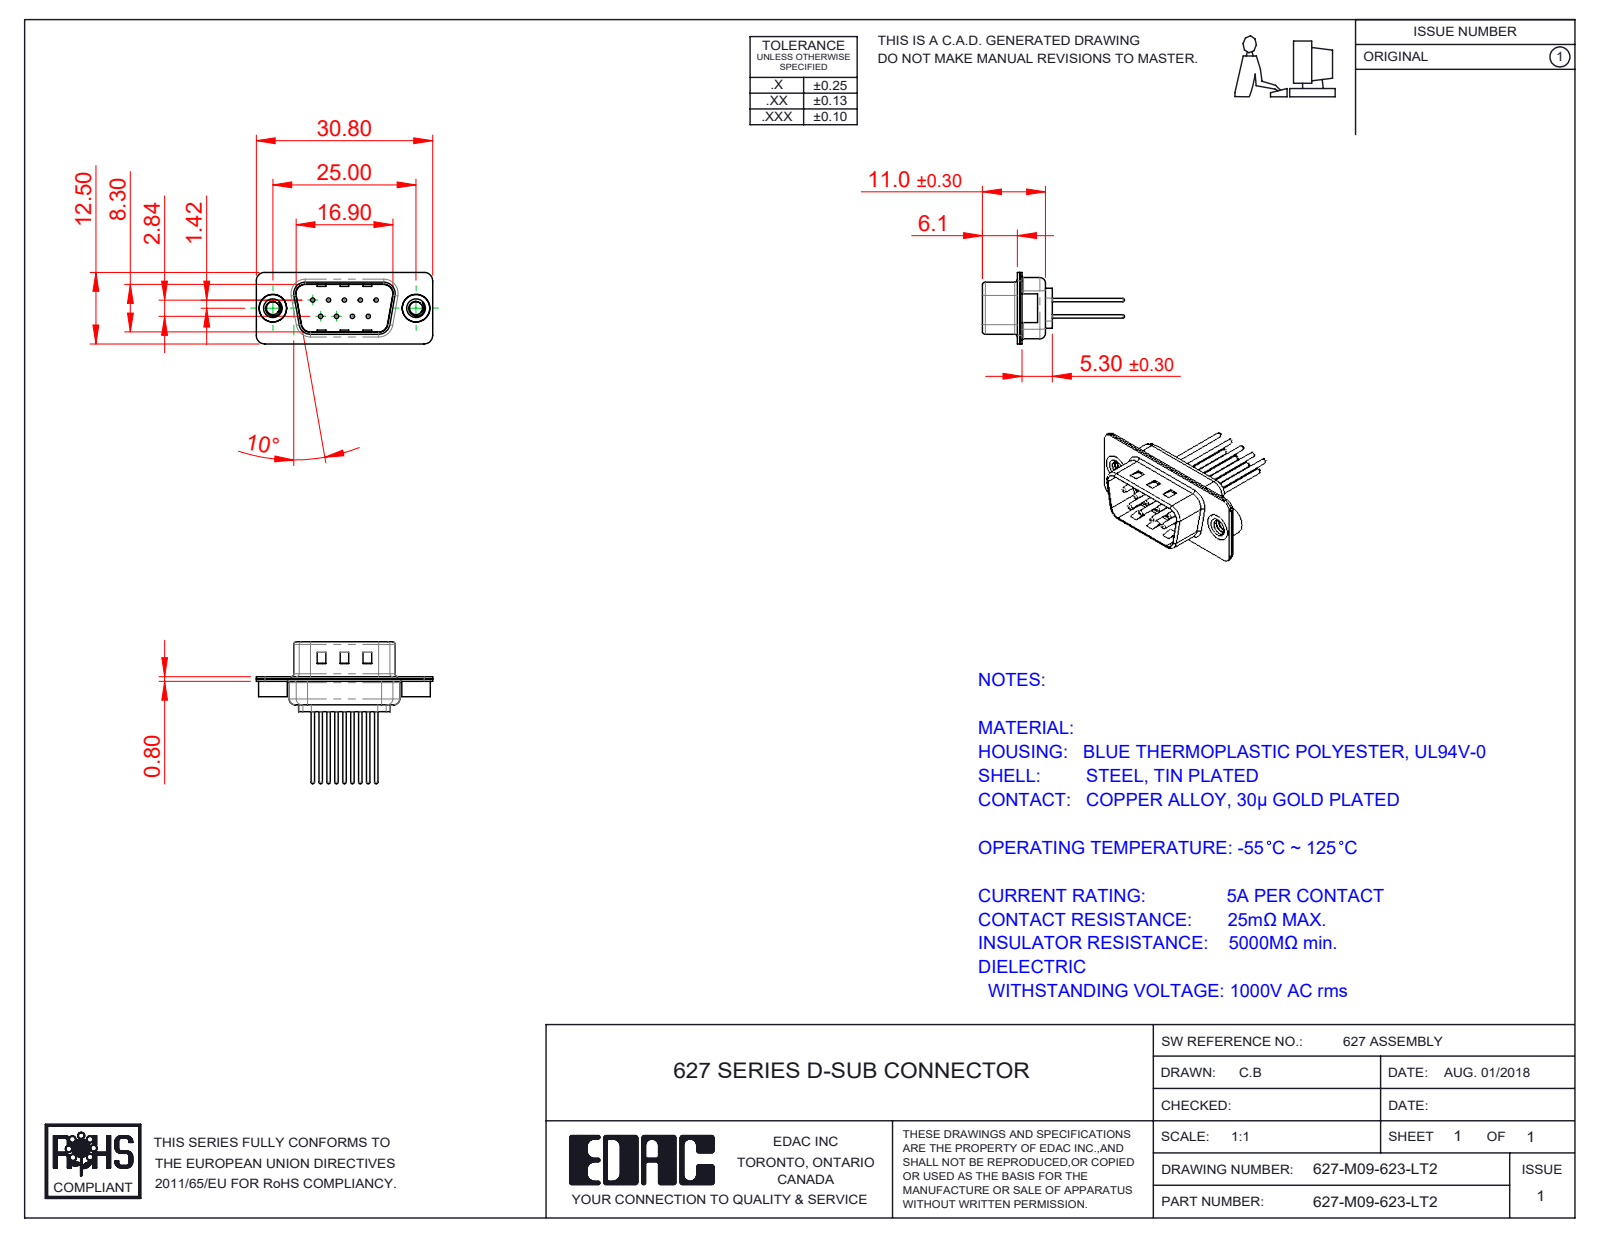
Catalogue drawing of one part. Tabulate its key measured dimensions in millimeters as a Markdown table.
| quantity | value |
| --- | --- |
| part name | 627M Contact Row 1_23; 627M Housing_09 Contacts; 627M Contact Row 2_23; 627M 4-40 Threaded Rivet (+3 more) |
| STEP written by | SolidWorks 2020 (CONFIG_CONTROL_DESIGN) |
| units | millimeters |
| bodies | 14 solids, 637 faces (170 planar, 255 cylindrical, 212 other) |
| overall size | 30.8 × 24.77 × 12.5 |
| volume | 1 328 mm³ |
| surface area | 3 691 mm² |
| round holes (diameter × count) | 0.75 × 9, 1.6 × 9, 2 × 9, 2.26 × 2, 4 × 2, 4.8 × 2 |
| round bosses / shafts (diameter × count) | 1.5 × 9, 0.6 × 9, 5 × 2, 4.9 × 2 |
| partial cylindrical surfaces (radius × count) | 1.5 × 16, 2 × 12, 0.5 × 8, 1.6 × 8, 0.25 × 4, 0.6 × 4, 0.65 × 4, 0.9 × 4 |
| main face-to-face distances | 0.4, 0.8, 9.5, 9.1, 8.7, 0.65, 9.9, 1.2, 6.1, 5.3 |
| hole center spacings | 3.16, 2.77, 5.54, 5.03, 5.04, 8.31, 7.1, 7.48 |
